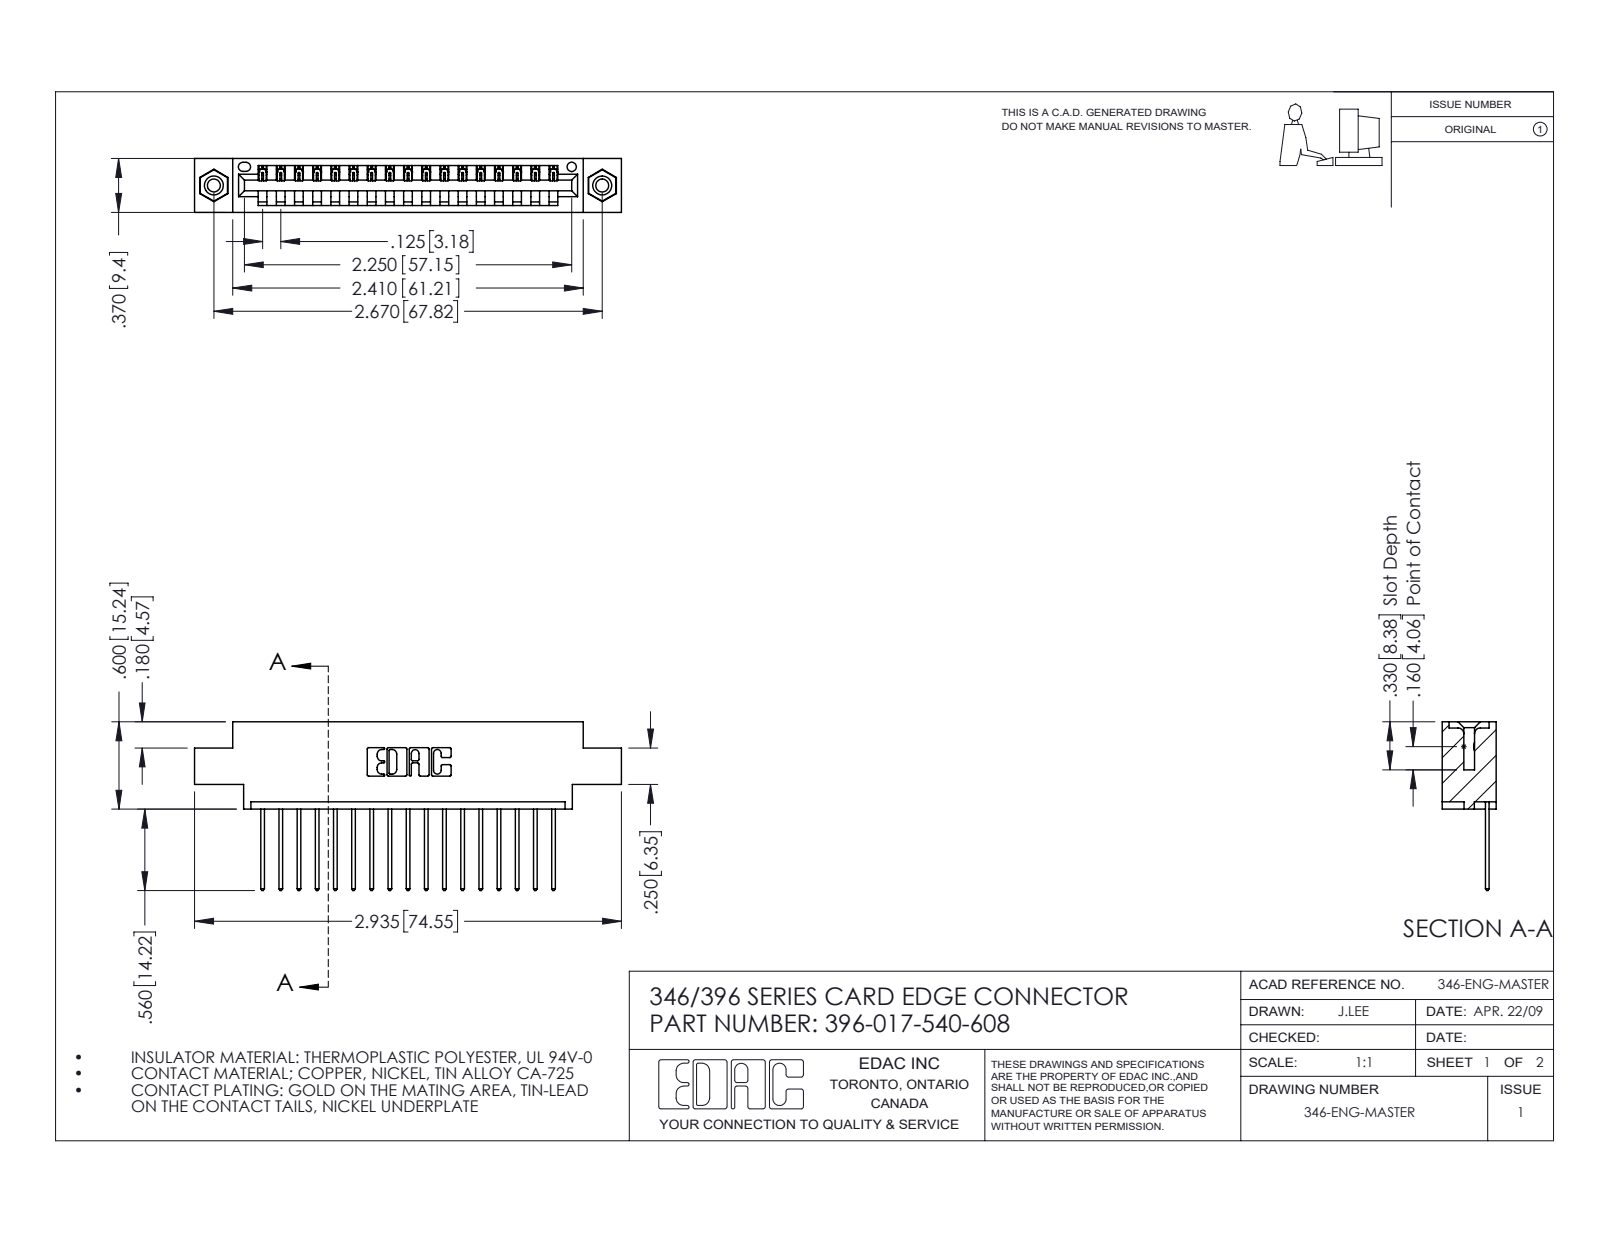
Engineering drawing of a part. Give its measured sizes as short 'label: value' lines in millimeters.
name: 345-292-001_345-293-140; 346 Part_0.170 Offset - 0.156 Dia-TI; 345-250-001_345-250-003-102; 396-017-540-608
written by: SolidWorks 2016 (CONFIG_CONTROL_DESIGN)
unit: mm
bodies: 20 solids, 1172 faces (792 planar, 364 cylindrical, 16 other)
size: 74.5 × 29.5 × 9.4
volume: 6 830 mm³; area: 8 613 mm²
holes: 2× ⌀2.3, 2× ⌀3.2, 2× ⌀4, 1× ⌀1.6
bosses: 2× ⌀3.9
rounds: 34× R0.2, 34× R0.3, 22× R0.3, 6× R0.2, 6× R0.8, 3× R0.7, 2× R0.8, 2× R1
face distances: 1.2, 8.2, 9.4, 6.4, 1.8, 7.6, 0.6, 5.6, 3.8, 2.5
hole spacings: 6.2, 62.6, 67.8
